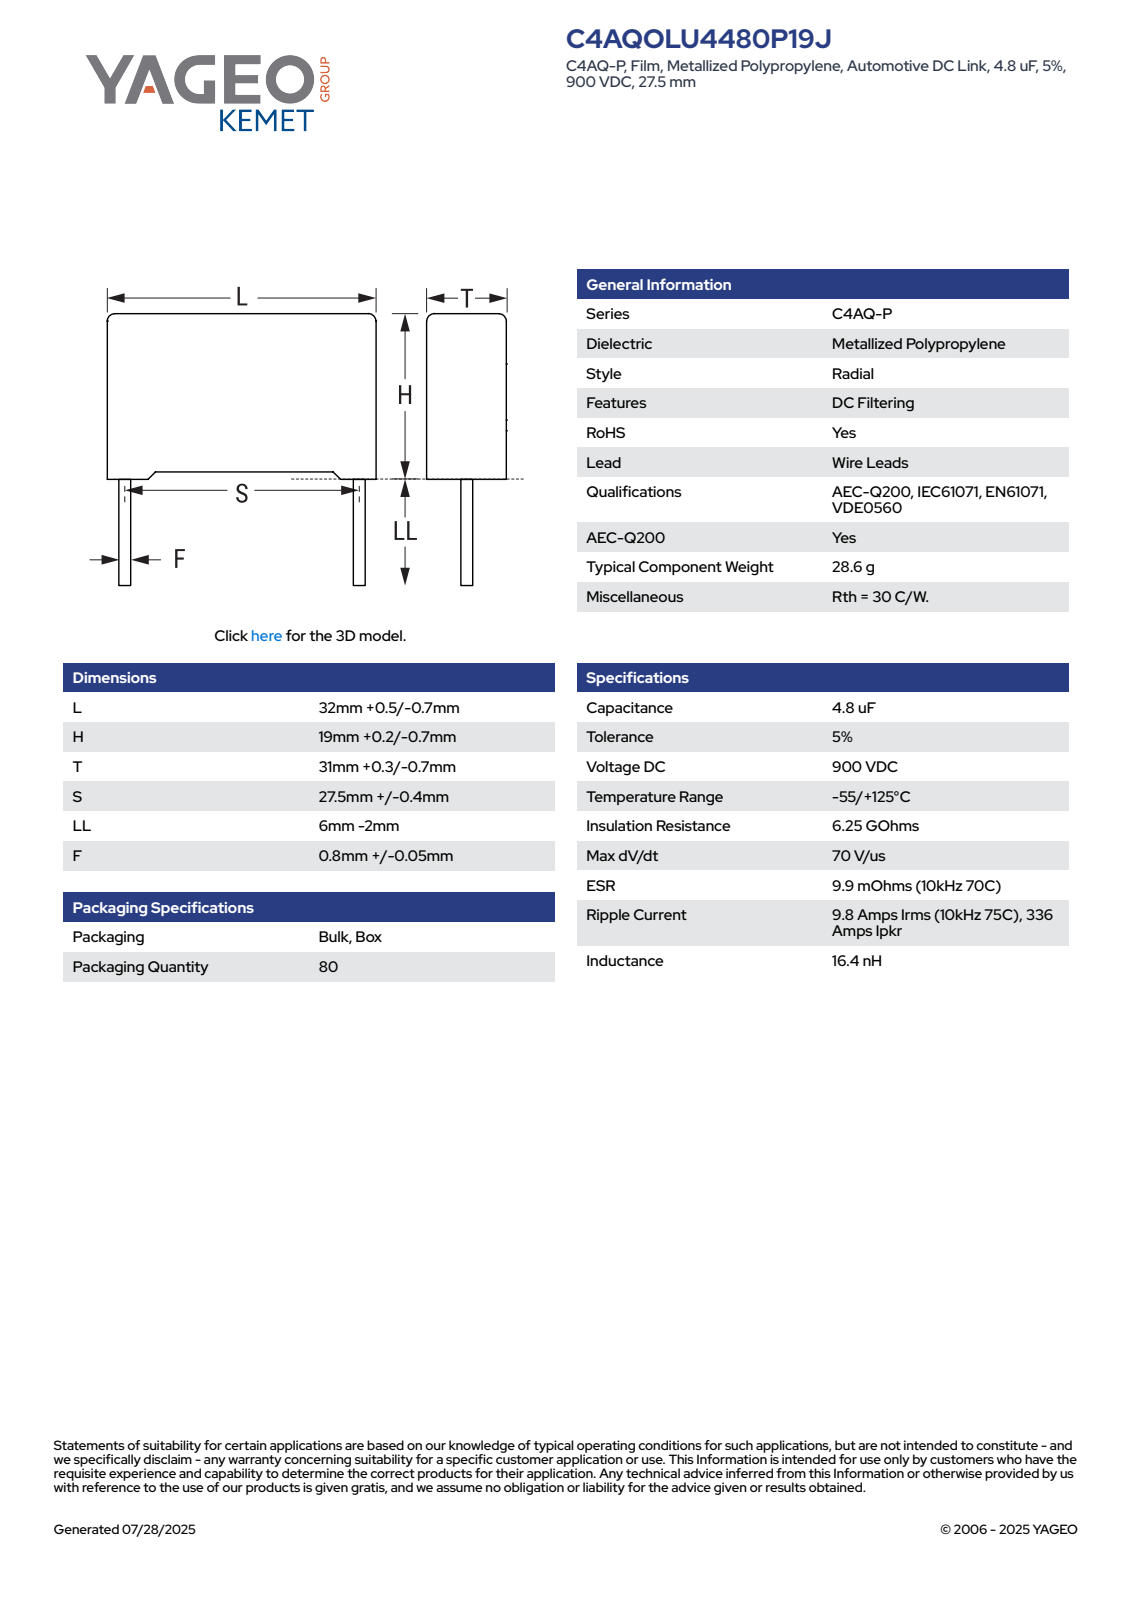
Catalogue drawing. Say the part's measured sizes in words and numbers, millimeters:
The part is named "CFR_RB2CFP_32X19X31_L32.5H19.2T31.3S27.5LL4F0.85". Its 3-D file was written by "SolidWorks 2014 (AUTOMOTIVE_DESIGN)". It is 4 solids with 85 faces: 77 planar, 8 cylindrical and 0 other. Overall it measures 32.5 by 31.3 by 23.2 millimeters. Its volume is 18 833 cubic millimeters and its surface area 4 589 square millimeters. Round bosses or shafts: 2 of diameter 0.85. Partial cylindrical surfaces (rounded edges, fillets, slot ends): 4 of radius 0.5. The main face-to-face distances are 18.45, 31.3, 32.5, 0.75, 19.2, 1.08, 0.66, 18.54, 31.42, 30.34.
